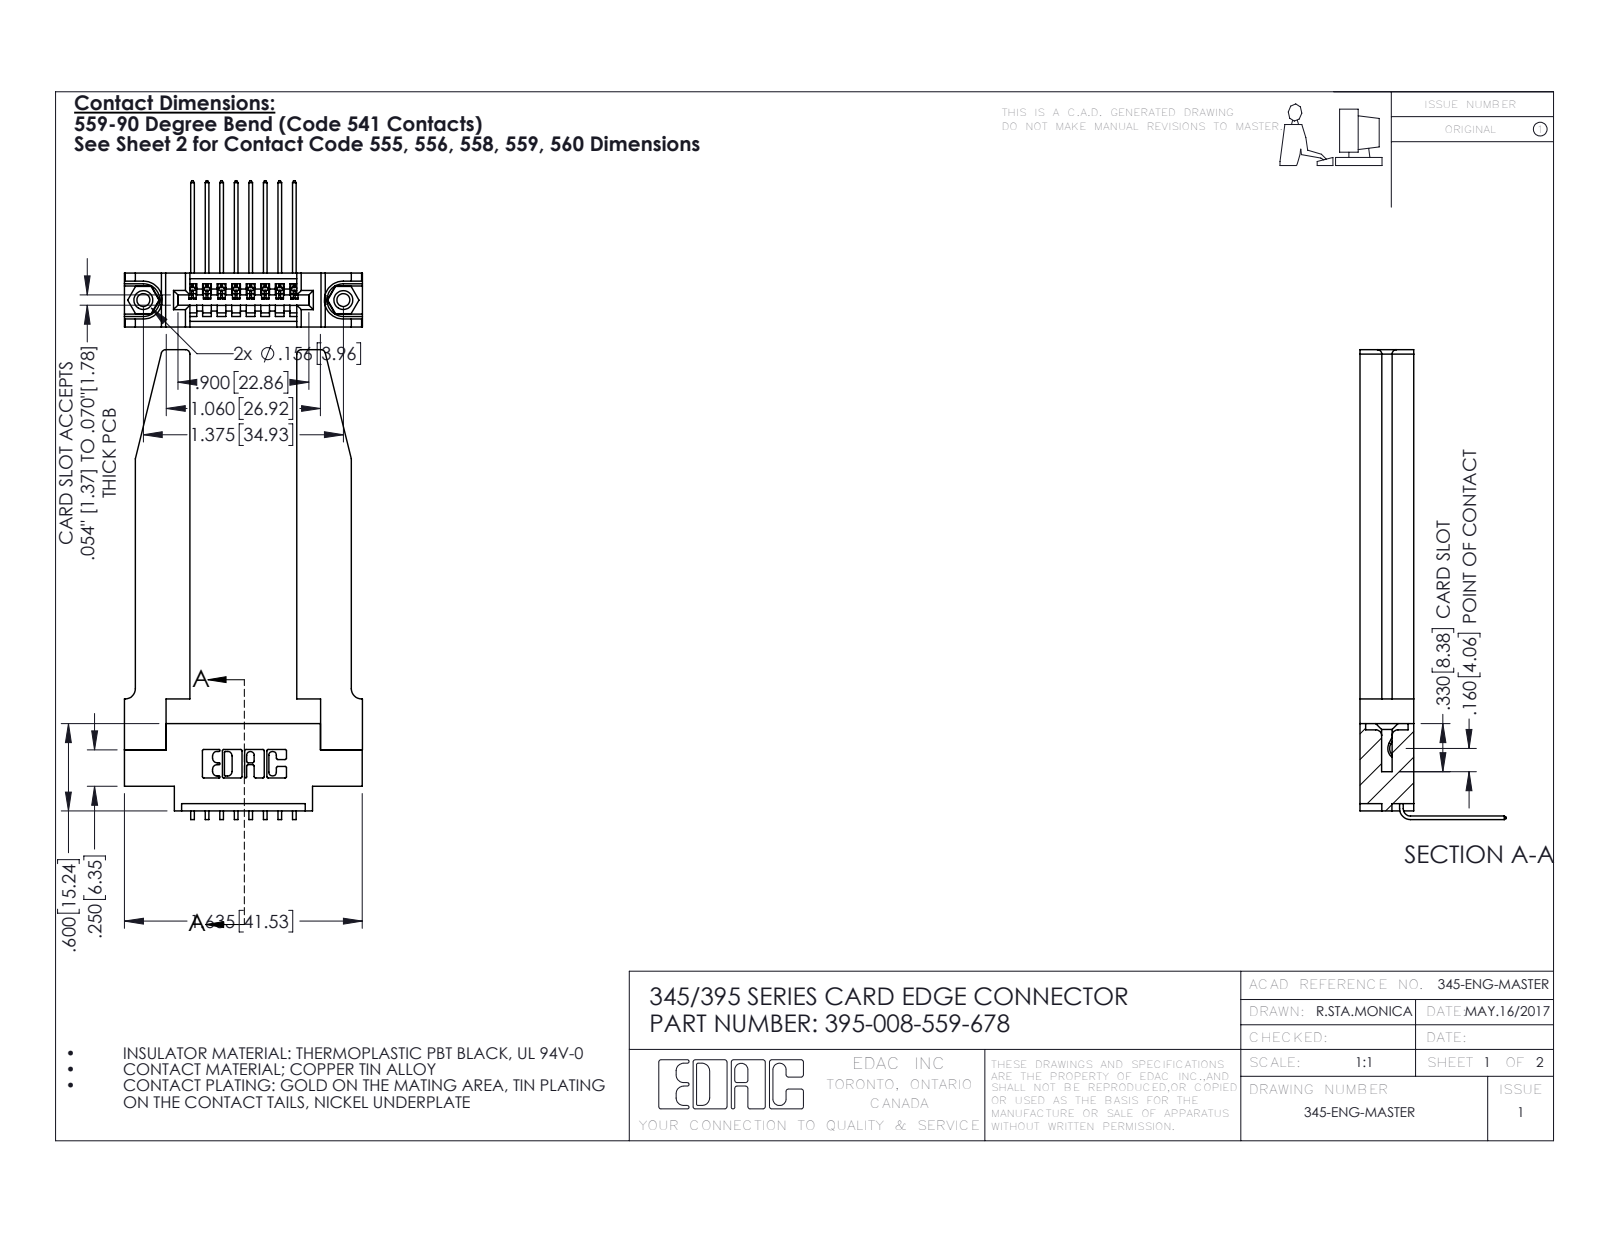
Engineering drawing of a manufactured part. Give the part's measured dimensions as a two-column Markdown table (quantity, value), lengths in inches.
| quantity | value |
| --- | --- |
| part name | 395-008-559-678; 345-292-001_558 559 Tail - 1; 345 Part_0.170 Offset - 0.156 Dia-TH; 345-220-078_345-220-078 (+1 more) |
| STEP written by | SolidWorks 2016 (CONFIG_CONTROL_DESIGN) |
| units | inches |
| bodies | 13 solids, 844 faces (562 planar, 230 cylindrical, 52 other) |
| overall size | 3.229 × 1.636 × 1.005 |
| volume | 0.693 in³ |
| surface area | 17.71 in² |
| round holes (diameter × count) | 0.089 × 2, 0.125 × 2, 0.156 × 2, 0.064 × 1 |
| round bosses / shafts (diameter × count) | 0.155 × 2 |
| partial cylindrical surfaces (radius × count) | 0.01 × 22, 0.006 × 16, 0.03 × 8, 0.007 × 6, 0.031 × 6, 0.026 × 3, 0.031 × 2, 0.04 × 2 |
| main face-to-face distances | 0.37, 0.15, 0.072, 0.22, 0.148, 0.298, 0.735, 0.077, 0.095, 0.071 |
| hole center spacings | 0.27, 1.144, 1.375 |
